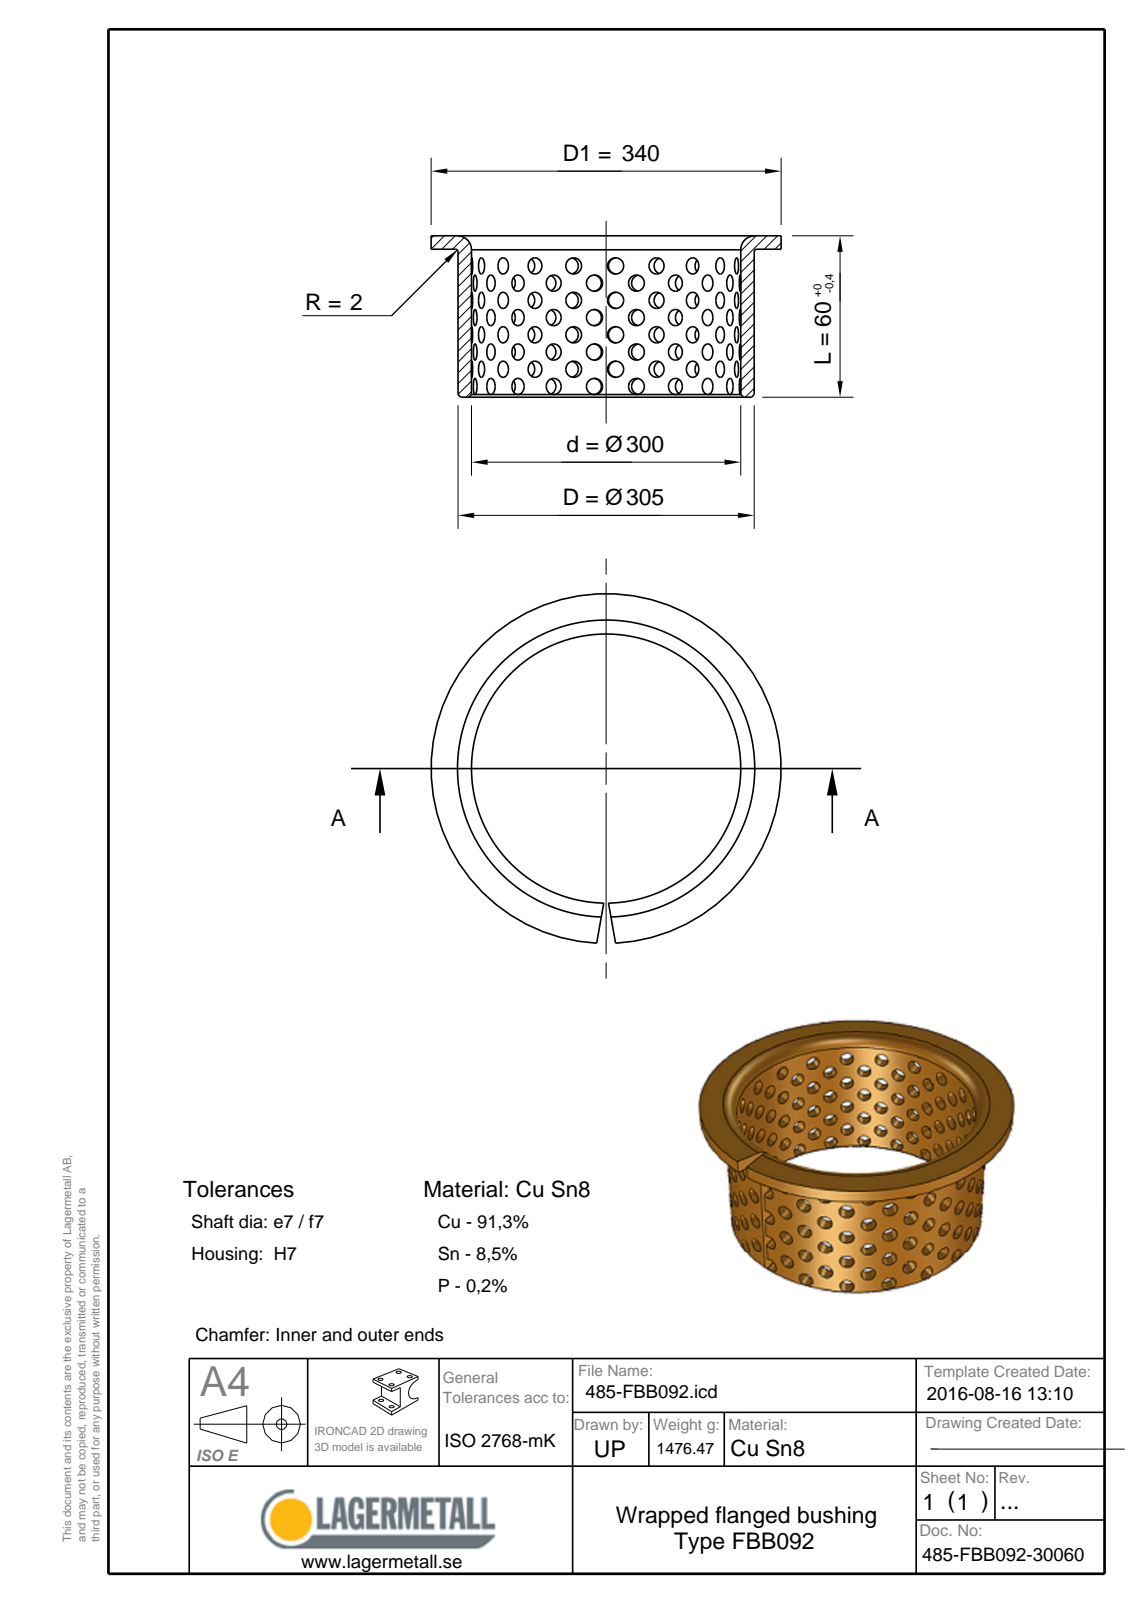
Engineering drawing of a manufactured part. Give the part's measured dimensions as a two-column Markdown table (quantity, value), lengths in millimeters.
| quantity | value |
| --- | --- |
| part name | 485-FBB092-30060 |
| STEP written by | Spatial InterOp 3D (CONFIG_CONTROL_DESIGN) |
| units | millimeters |
| bodies | 1 solid, 12 faces (5 planar, 3 cylindrical, 4 other) |
| overall size | 340 × 339.95 × 60 |
| volume | 182 280 mm³ |
| surface area | 150 973 mm² |
| round holes (diameter × count) | 300 × 1 |
| round bosses / shafts (diameter × count) | 340 × 1, 305 × 1 |
| main face-to-face distances | 2.5, 57.5, 60 |
